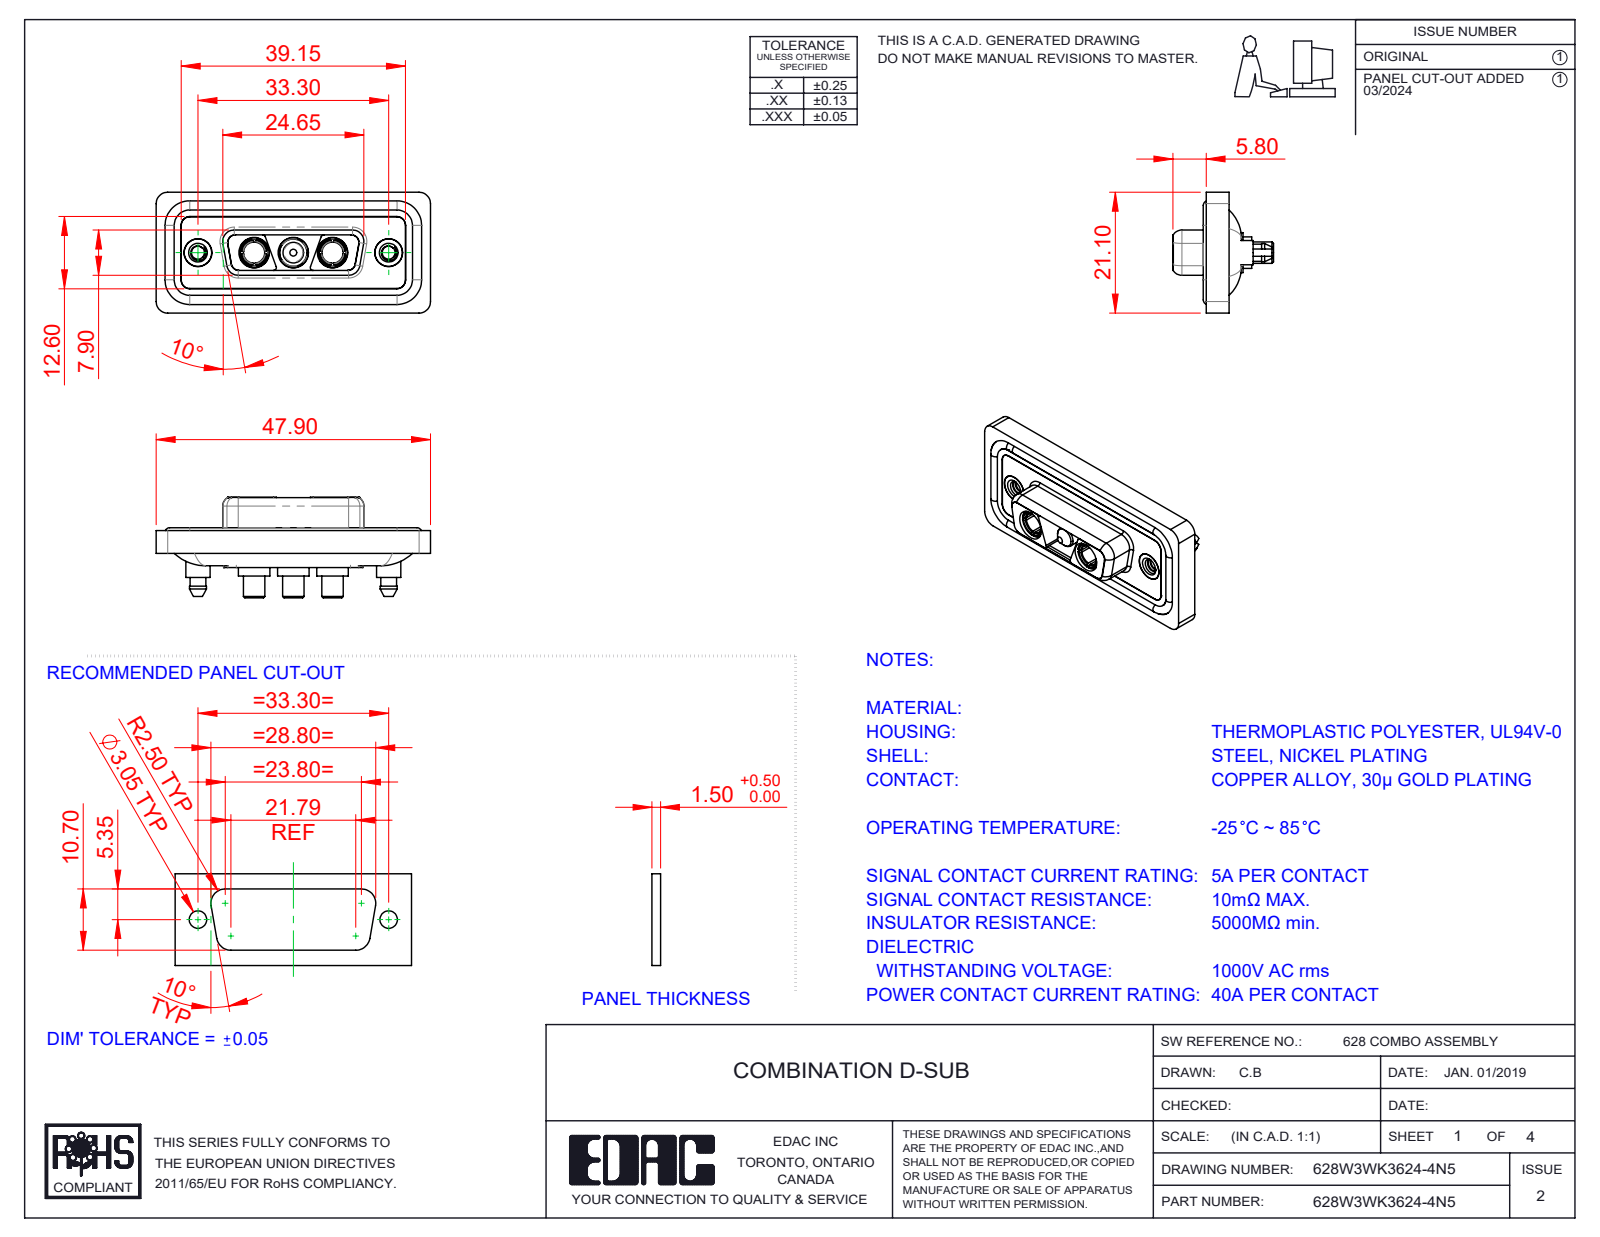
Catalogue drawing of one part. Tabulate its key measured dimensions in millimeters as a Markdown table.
| quantity | value |
| --- | --- |
| part name | 628Combo Shell Front_15 Contacts; Power Pin_40A S; 628W3WK3624-4N5; 628Combo Waterproof Housing_15 Contacts (+4 more) |
| STEP written by | SolidWorks 2023 (CONFIG_CONTROL_DESIGN) |
| units | millimeters |
| bodies | 13 solids, 633 faces (194 planar, 290 cylindrical, 149 other) |
| overall size | 47.9 × 21.1 × 17.55 |
| volume | 6 067 mm³ |
| surface area | 9 870 mm² |
| round holes (diameter × count) | 4.85 × 5, 5.3 × 3, 2.26 × 2, 3.7 × 2, 4 × 2, 4.05 × 2, 5 × 2 |
| round bosses / shafts (diameter × count) | 1.6 × 4, 5.5 × 3, 5.2 × 3, 4.75 × 3, 3.75 × 3, 5.4 × 2, 4.96 × 2, 4.95 × 2 |
| partial cylindrical surfaces (radius × count) | 1.5 × 24, 2 × 20, 1.35 × 12, 1.6 × 10, 0.5 × 8, 0.25 × 4, 0.6 × 4, 0.65 × 4 |
| main face-to-face distances | 0.4, 1.6, 0.5, 1.8, 1.1, 2.9, 5.65, 7.05, 5.35, 1.5 |
| hole center spacings | 6.85, 9.8, 16.65, 23.5, 13.7, 33.3 |
